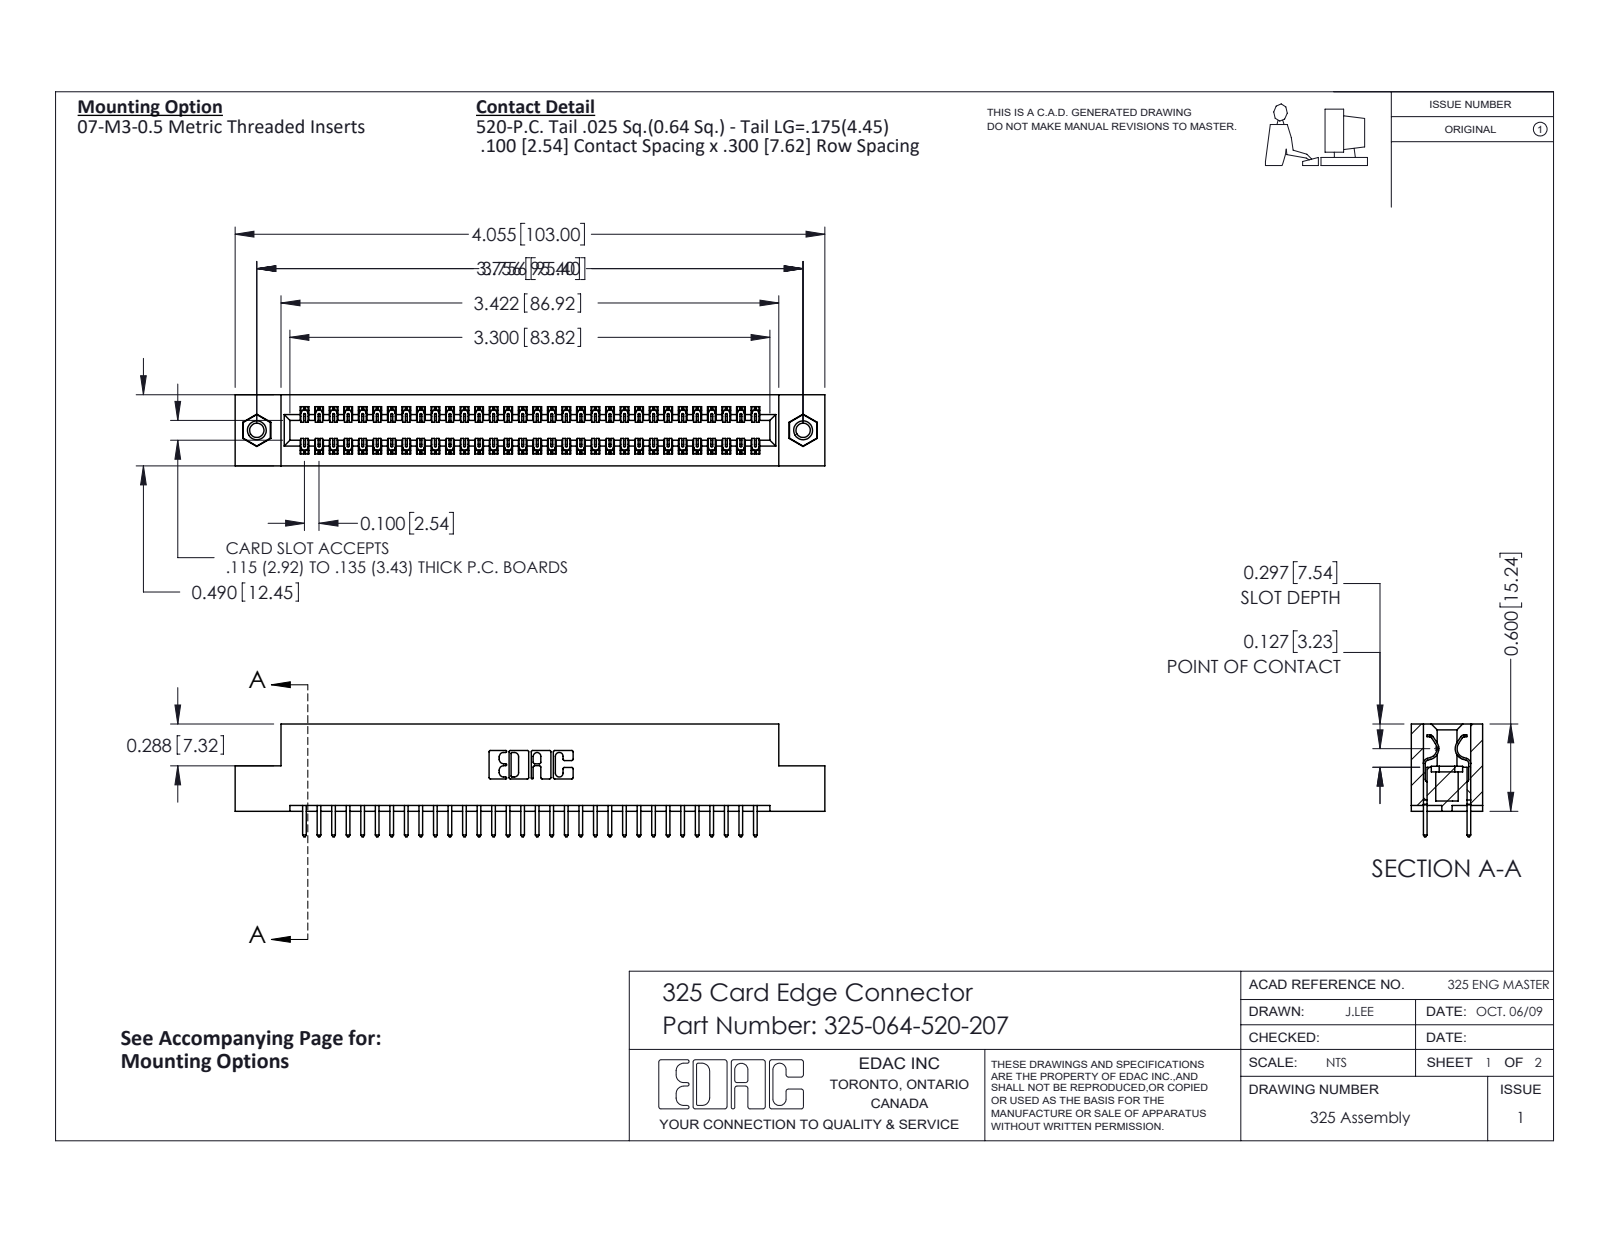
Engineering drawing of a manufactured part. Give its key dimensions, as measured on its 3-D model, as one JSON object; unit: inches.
{"part_name": "345-250-001_345-250-005-103; 325-064-520-207; 325-292-001_325-293-120; 325 Part_TI", "step_written_by": "SolidWorks 2016 (CONFIG_CONTROL_DESIGN)", "units": "inches", "bodies": {"solids": 67, "faces": 3502, "planar": 2406, "cylindrical": 1080, "other": 16}, "overall_size": [4.055, 0.775, 0.49], "volume_in3": 0.805, "surface_area_in2": 24.21, "round_holes": [[0.098, 2], [0.125, 2], [0.16, 2]], "round_bosses_or_shafts": [[0.155, 2]], "partial_cylinders_radius": [[0.006, 96], [0.01, 64], [0.01, 22], [0.007, 6], [0.031, 6], [0.026, 3], [0.014, 2], [0.022, 2]], "face_to_face_distances": [0.083, 0.407, 0.3, 0.49, 0.107, 0.383, 0.025, 0.325, 0.275, 0.04], "hole_center_spacings": [3.756]}
